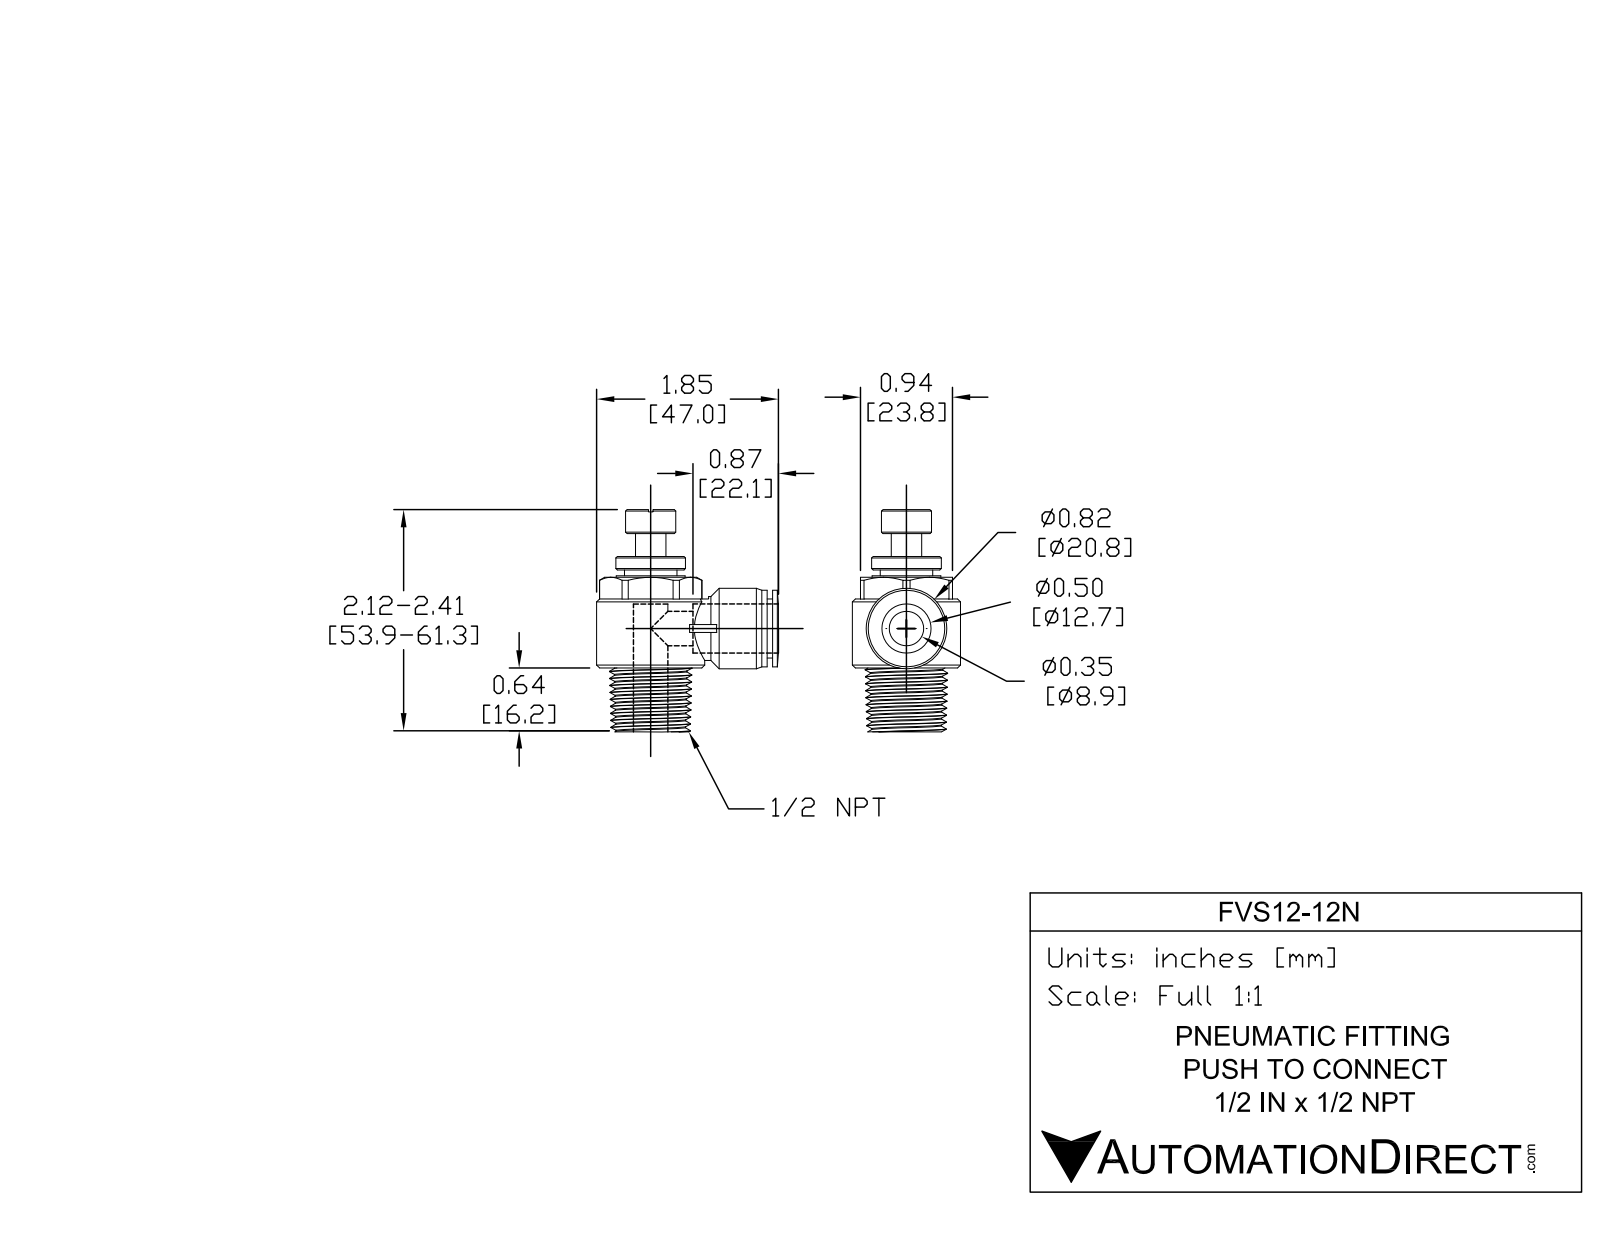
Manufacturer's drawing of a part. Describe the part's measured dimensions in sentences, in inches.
The part is named "FVS12-12N". Its 3-D file was written by "SolidWorks 2015 (AUTOMOTIVE_DESIGN)". It is 1 solid with 579 faces: 259 planar, 150 cylindrical and 170 other. Overall it measures 2.413 by 1.986 by 1.102 inches. Its volume is 1.481 cubic inches and its surface area 14.31 square inches. Round holes: 2 of diameter 0.315, 1 of diameter 0.51. Round bosses or shafts: 1 of diameter 1.102, 1 of diameter 0.945, 1 of diameter 0.864, 1 of diameter 0.819, 1 of diameter 0.787, 1 of diameter 0.783, 1 of diameter 0.713, 1 of diameter 0.65. Partial cylindrical surfaces (rounded edges, fillets, slot ends): 1 of radius 0.256, 1 of radius 0.354, 1 of radius 0.512. The main face-to-face distances are 1.622, 0.697, 0.925, 1.831, 1.134, 0.209, 0.945, 0.051, 1.693, 0.996.
